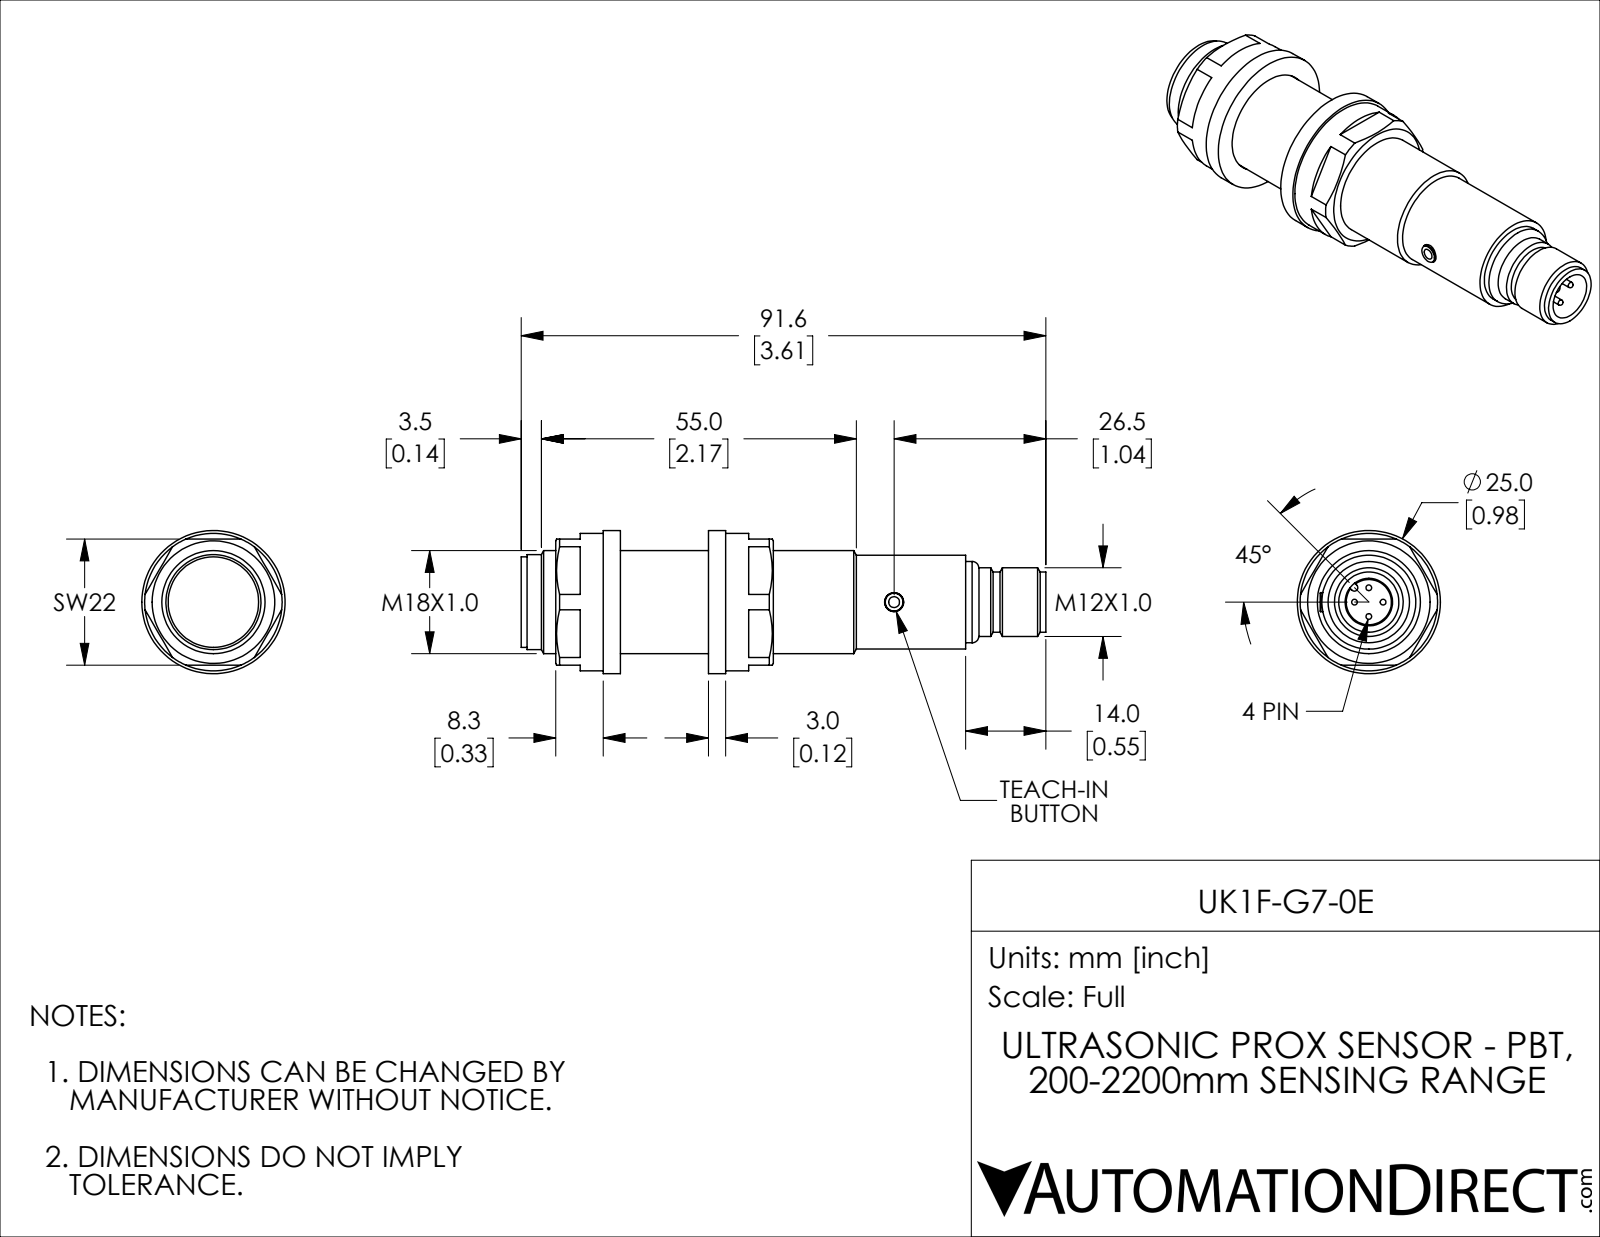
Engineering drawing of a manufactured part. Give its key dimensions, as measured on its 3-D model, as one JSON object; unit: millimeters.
{"part_name": "UK1F-G7-0E", "step_written_by": "SolidWorks 2018 (AUTOMOTIVE_DESIGN)", "units": "millimeters", "bodies": {"solids": 6, "faces": 123, "planar": 43, "cylindrical": 49, "other": 31}, "overall_size": [91.6, 25, 25], "volume_mm3": 24200, "surface_area_mm2": 10330, "round_holes": [[3.3, 1], [8.3, 1], [18, 1], [18.2, 1]], "round_bosses_or_shafts": [[1, 4], [25, 1], [24, 1], [16.6, 1], [16.4, 1], [15.8, 1], [14.2, 1], [12, 1]], "partial_cylinders_radius": [[0.6, 1]], "face_to_face_distances": [3, 18.4, 21.4, 15.4, 22, 8.3, 11.3, 26.7, 29.7, 14.3]}
